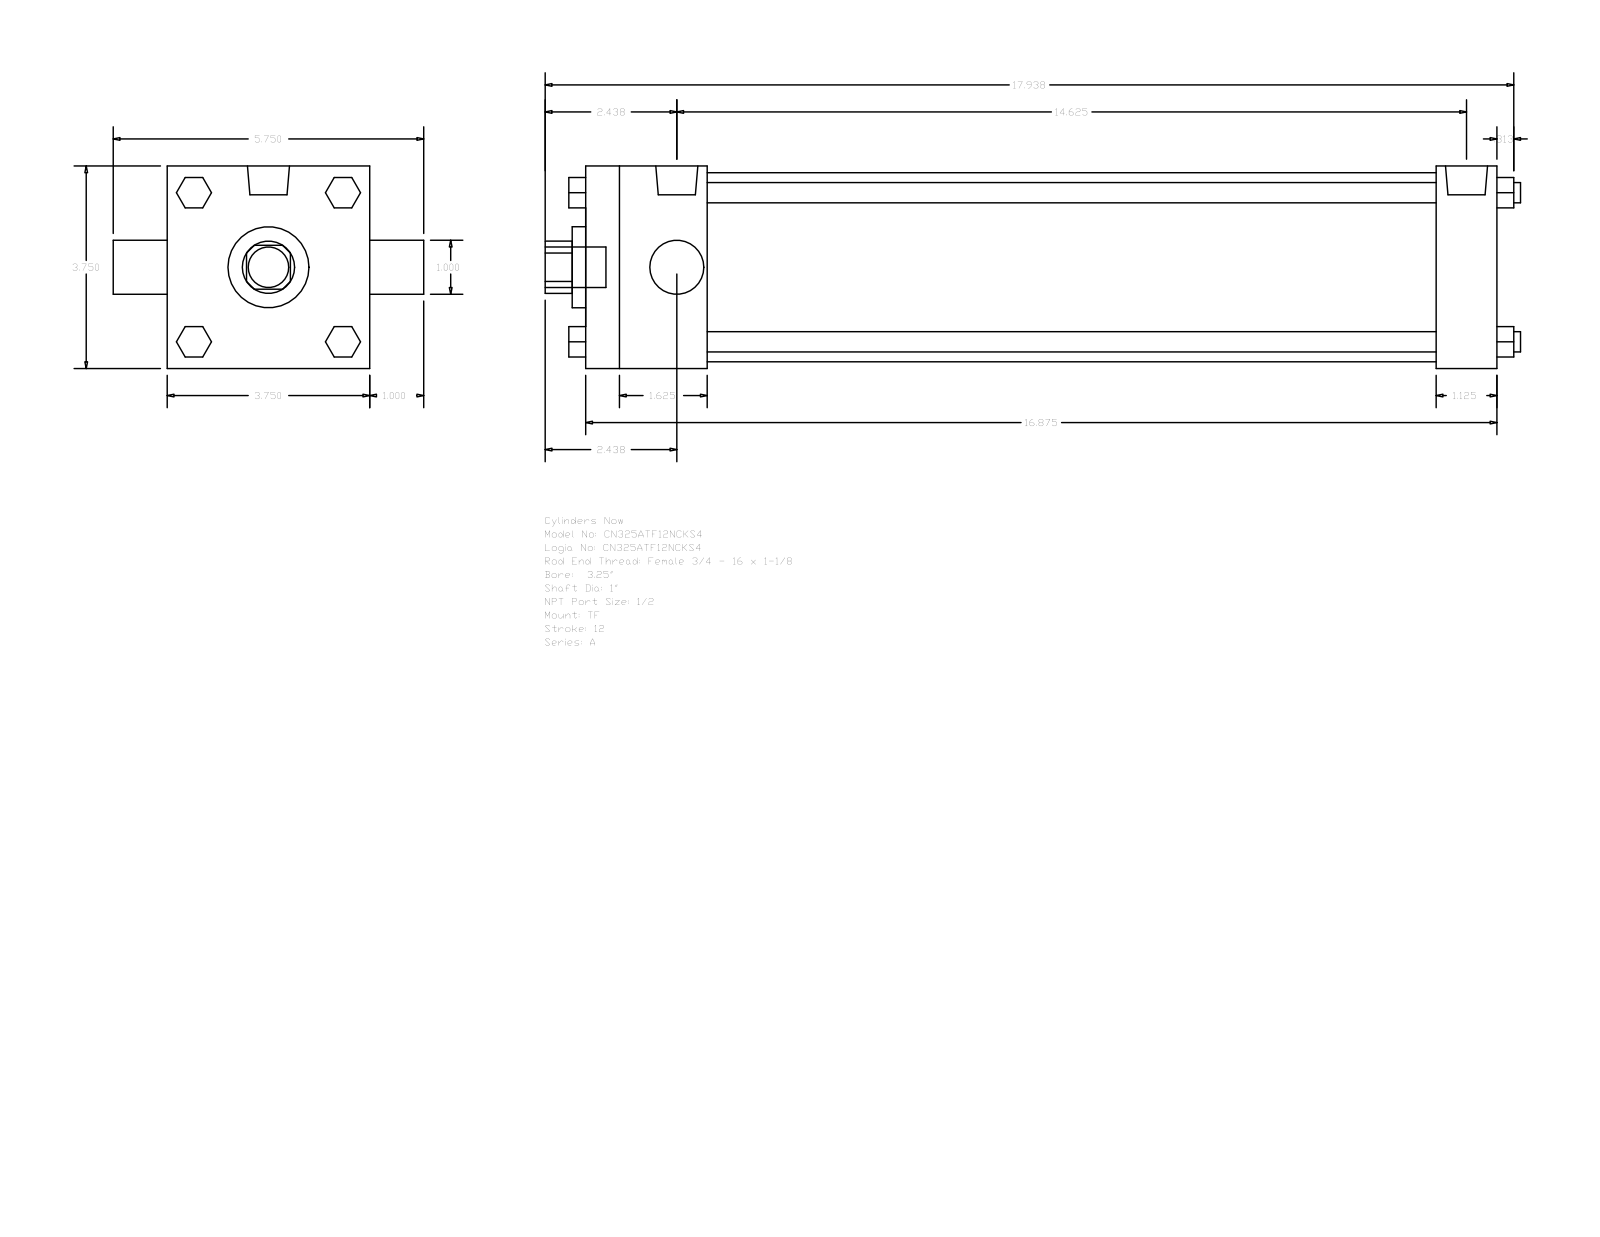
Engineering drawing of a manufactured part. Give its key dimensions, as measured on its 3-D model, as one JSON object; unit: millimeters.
{"part_name": "A_TF__0325_1", "step_written_by": "GSSL Pune (CONFIG_CONTROL_DESIGN)", "units": "millimeters", "bodies": {"solids": 0, "faces": 120, "planar": 92, "cylindrical": 28, "other": 0}, "overall_size": [458.79, 146.05, 95.25], "round_holes": [[25.4, 2], [38.1, 1], [88.9, 1]], "round_bosses_or_shafts": [[9.53, 4], [8.73, 3], [19.77, 2], [19.05, 1]], "partial_cylinders_radius": [[12.29, 1]], "face_to_face_distances": [95.24, 428.63, 57.15, 400.05, 342.9, 371.48, 28.58, 14.28, 35.05, 60.71]}
